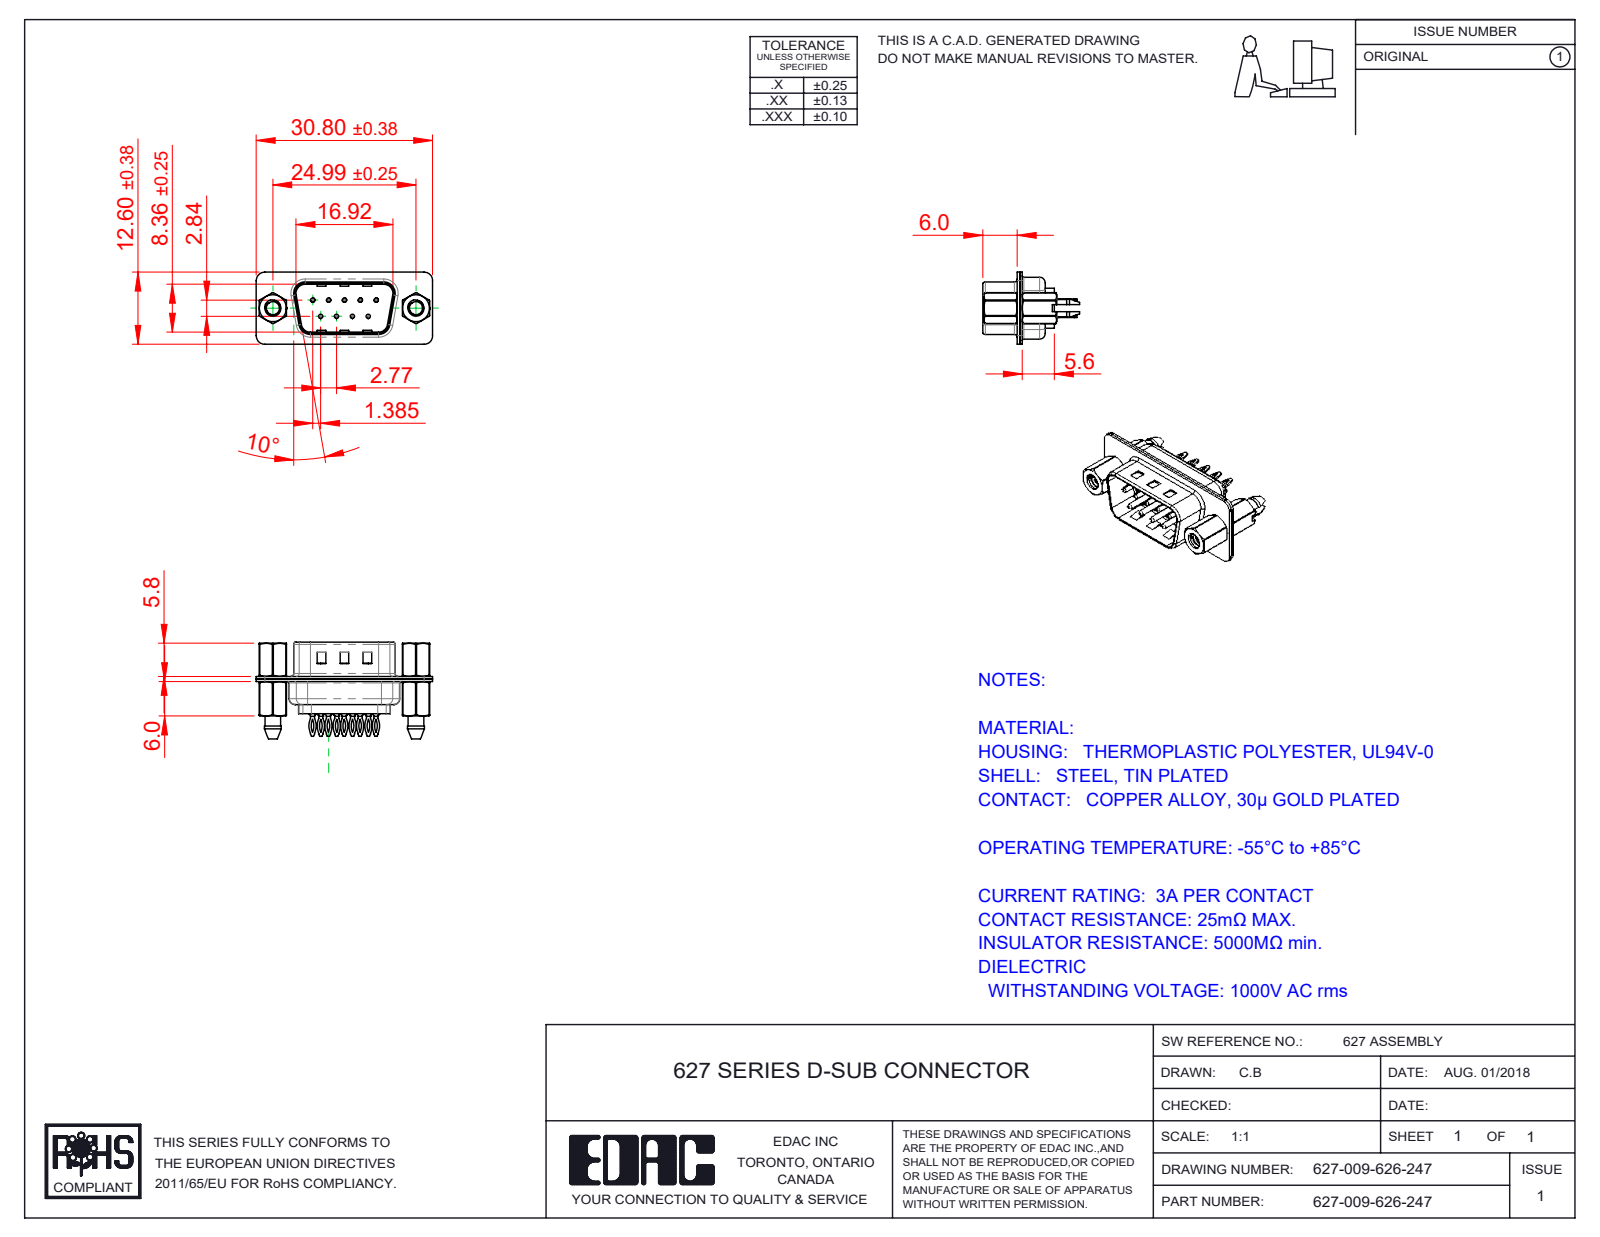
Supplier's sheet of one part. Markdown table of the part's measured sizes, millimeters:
| quantity | value |
| --- | --- |
| part name | 627 Shell Front_09 Contacts; 627 Contact Row 1_26L; 627-009-626-047; 627 Housing_09 LP (+4 more) |
| STEP written by | SolidWorks 2020 (CONFIG_CONTROL_DESIGN) |
| units | millimeters |
| bodies | 16 solids, 1188 faces (341 planar, 512 cylindrical, 335 other) |
| overall size | 30.8 × 16.9 × 12.6 |
| volume | 1 639 mm³ |
| surface area | 4 680 mm² |
| round holes (diameter × count) | 0.35 × 9, 1.1 × 9, 1.6 × 9, 2.26 × 2, 2.29 × 2, 4 × 2, 4.8 × 2 |
| round bosses / shafts (diameter × count) | 2 × 9, 1.5 × 9, 0.75 × 9, 4.9 × 2, 2.79 × 2 |
| partial cylindrical surfaces (radius × count) | 1.5 × 20, 2.92 × 18, 3.33 × 18, 2 × 12, 1.6 × 10, 0.5 × 8, 0.25 × 4, 0.6 × 4 |
| main face-to-face distances | 0.45, 0.4, 0.9, 0.82, 9.58, 1.4, 4.76, 8.76, 6.5, 0.5 |
| hole center spacings | 3.16, 2.77, 5.54, 5.03, 5.04, 8.31, 7.48, 7.49 |
